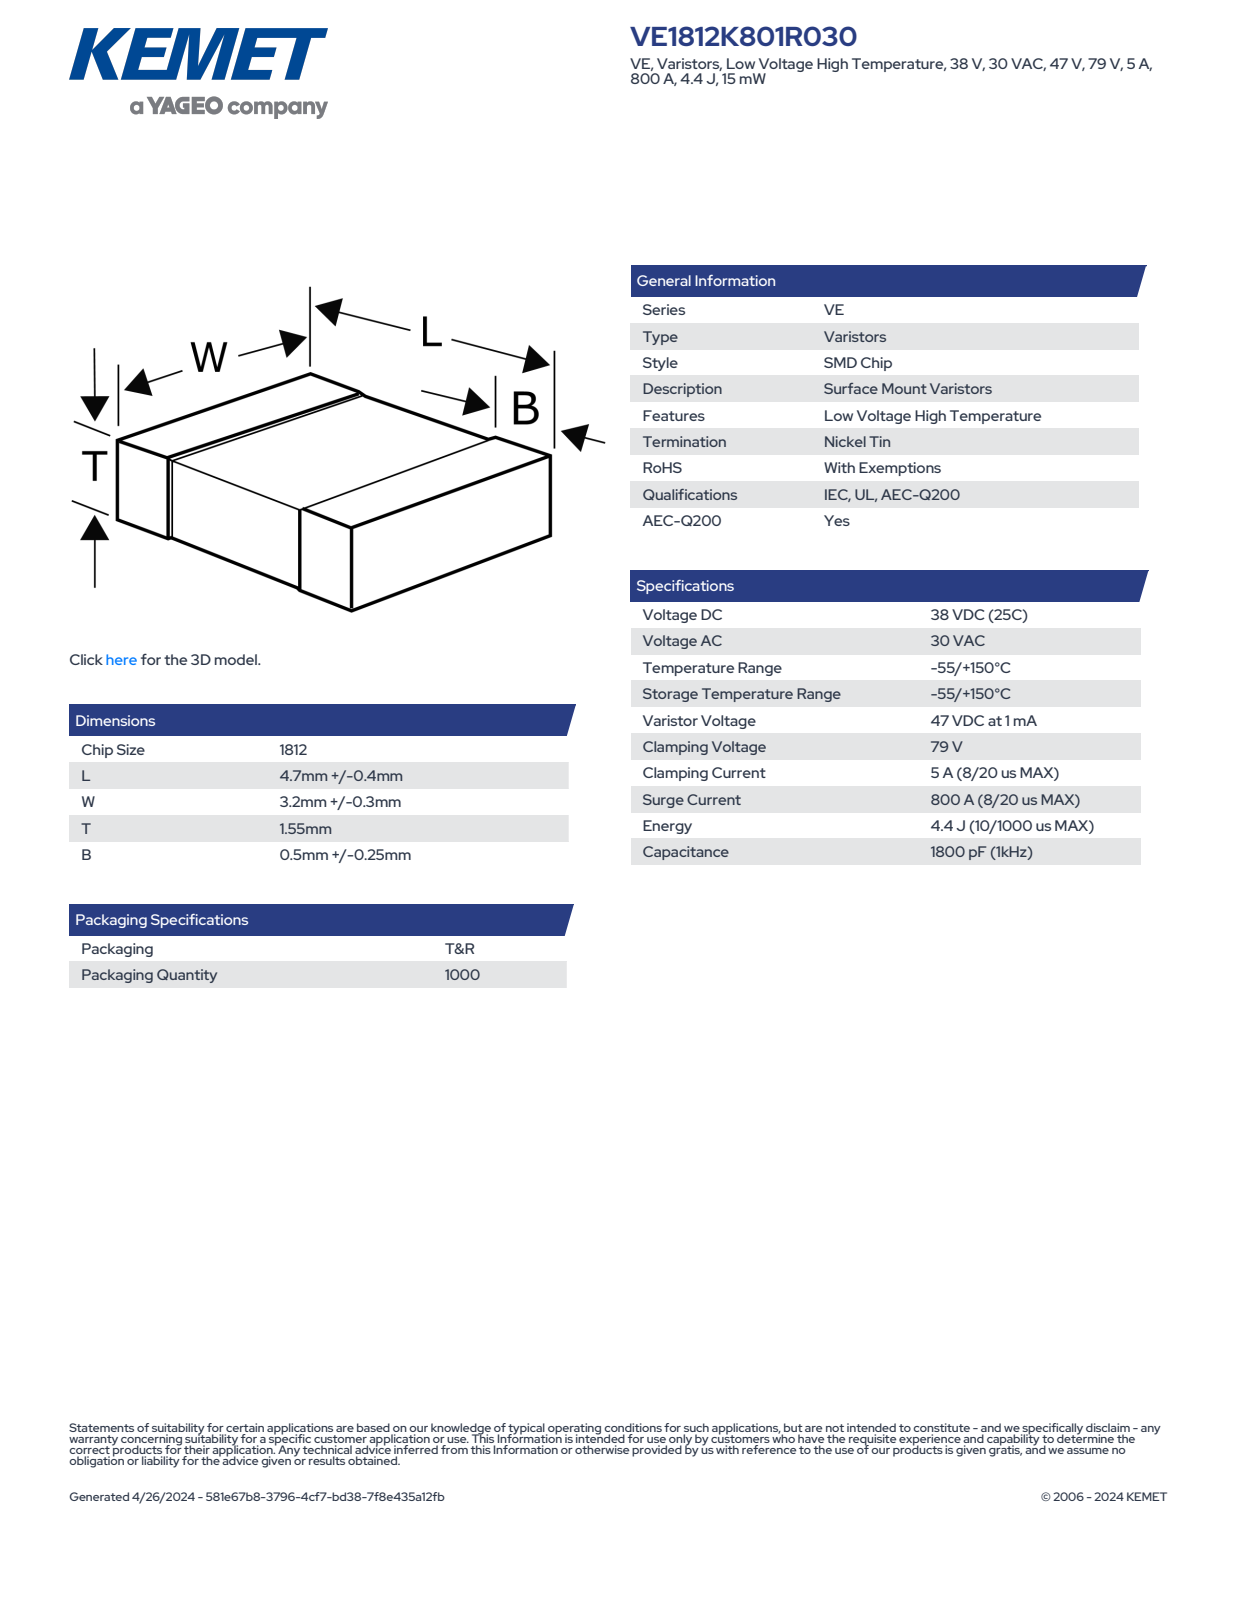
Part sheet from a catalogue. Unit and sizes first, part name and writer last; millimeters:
Units: millimetres
Overall size (bounding box): 5.1 × 3.5 × 1.55
Main face-to-face distances: 1.41, 1.48, 5.1, 3.36, 1.55, 3.43, 3.5, 2.24, 2.86, 2.75
Volume: 25 mm³ · Surface area: 61 mm²
Bodies: 4 solids, 125 faces (71 planar, 38 cylindrical, 16 other)
Part name (STEP PRODUCT): VS_SMD_1812_L5.10W3.5T1.55B0.75
STEP written by: SolidWorks 2014 (AUTOMOTIVE_DESIGN)
